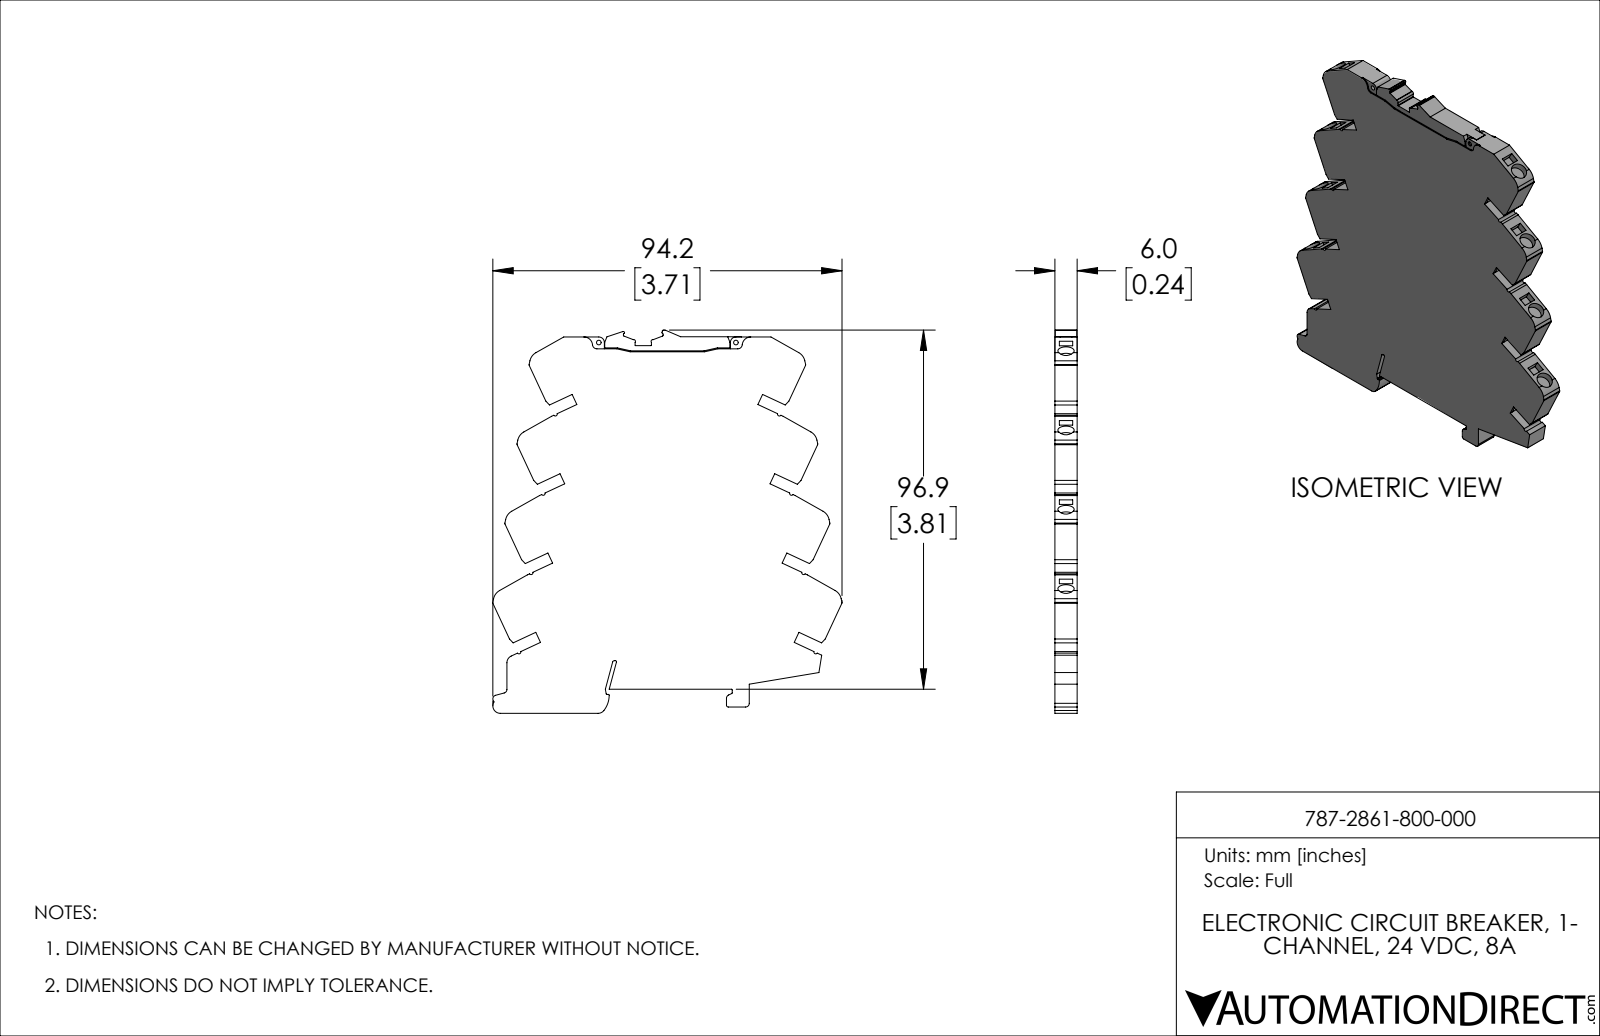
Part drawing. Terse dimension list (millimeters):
name: 787-2861/800-000
written by: PARTsolutions (CONFIG_CONTROL_DESIGN)
unit: mm
bodies: 1 solid, 294 faces (219 planar, 75 cylindrical, 0 other)
size: 103.36 × 94.26 × 6
volume: 43 932 mm³; area: 19 262 mm²
holes: 8× ⌀4.4, 2× ⌀1.25
rounds: 12× R0.5, 11× R0.2, 8× R0.4, 8× R3.35, 4× R1, 3× R0.3, 3× R2, 2× R0.45
face distances: 6, 17.99, 17.02, 12.01, 5.9, 12, 3, 24.01, 35.98, 6.5
hole spacings: 13.35, 13.34, 26.7, 26.69, 26.71, 37, 40.04, 40.05
